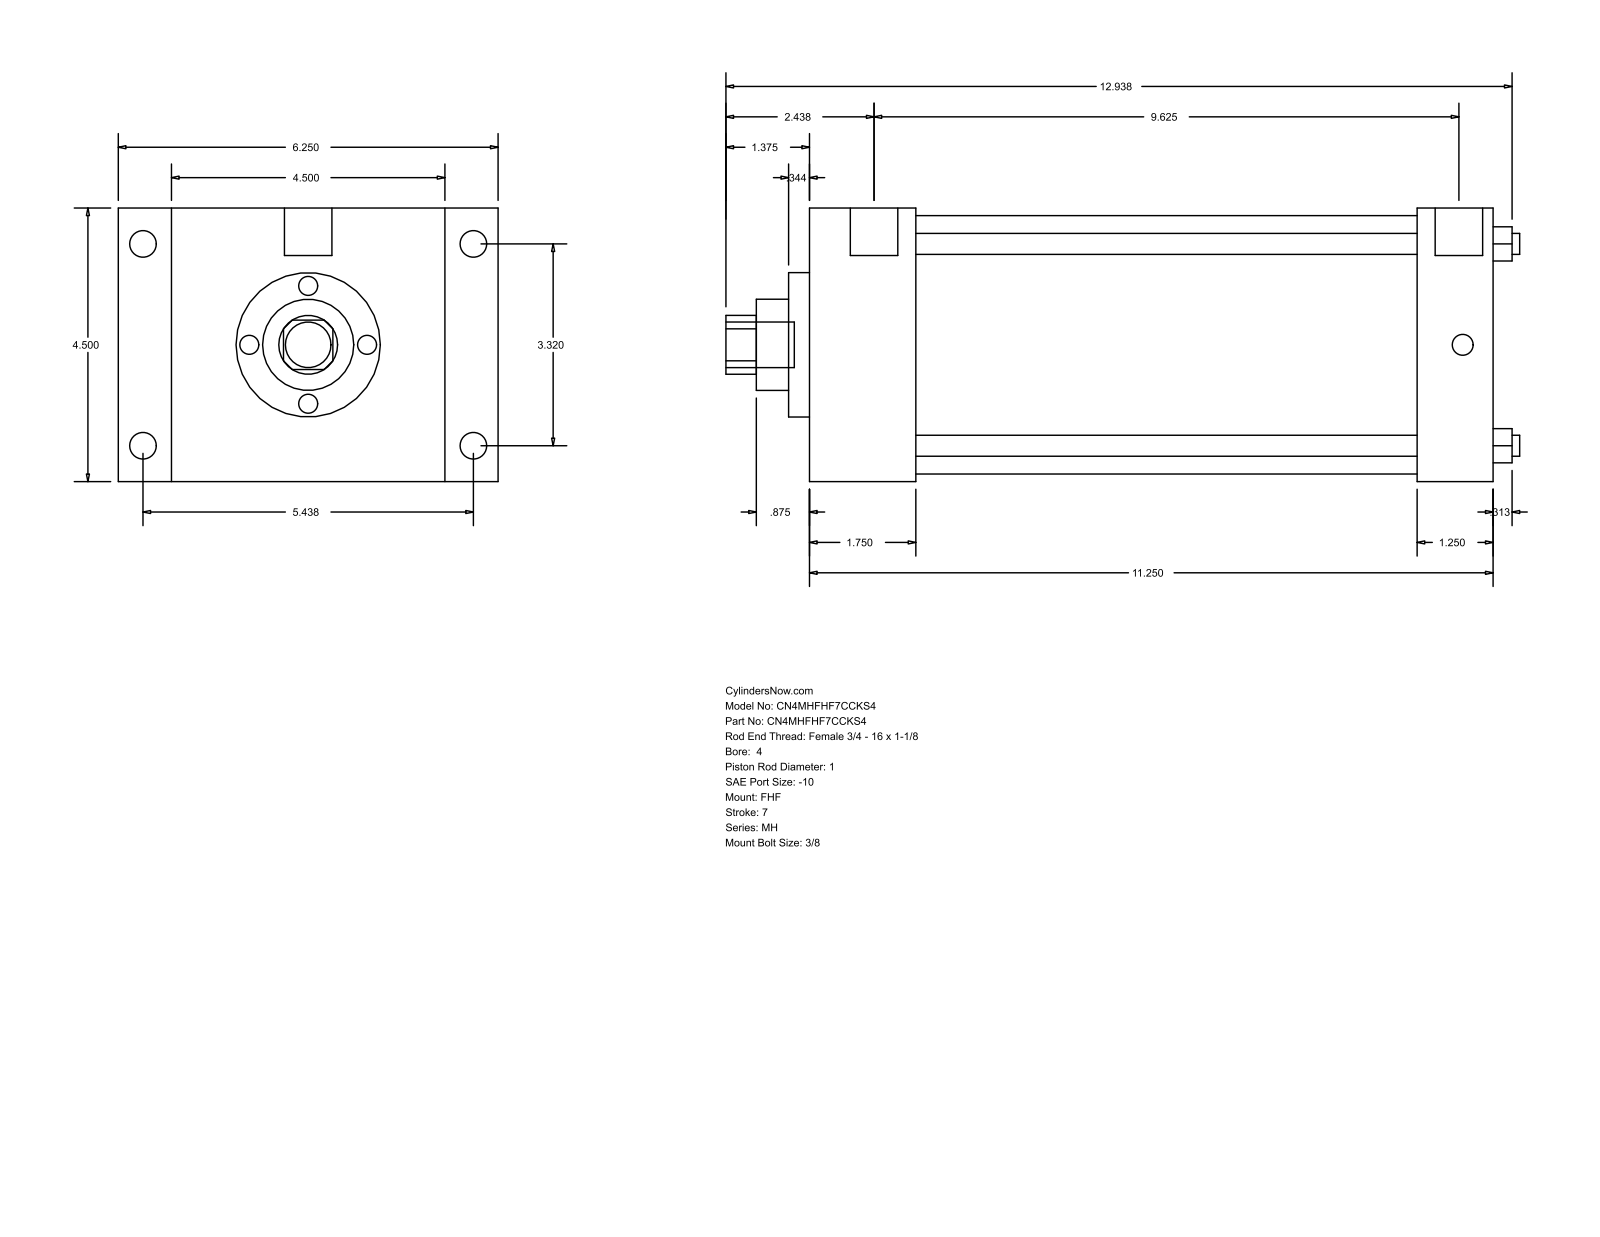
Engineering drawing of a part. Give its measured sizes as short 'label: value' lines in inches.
name: MH_FHF__0400_1
written by: GSSL Pune (CONFIG_CONTROL_DESIGN)
unit: in
bodies: 0 solids, 90 faces (61 planar, 29 cylindrical, 0 other)
size: 13.063 × 6.25 × 4.5
holes: 4× ⌀0.345, 1× ⌀1, 1× ⌀1.5, 1× ⌀2.375, 1× ⌀4.25
bosses: 4× ⌀0.438, 4× ⌀0.344, 2× ⌀0.781, 1× ⌀0.75
rounds: 1× R0.484
face distances: 4.5, 11.25, 1.75, 9.5, 0.875, 5.375, 6.25, 10, 8.25, 1.25
hole spacings: 2.347, 3.32, 4.695
